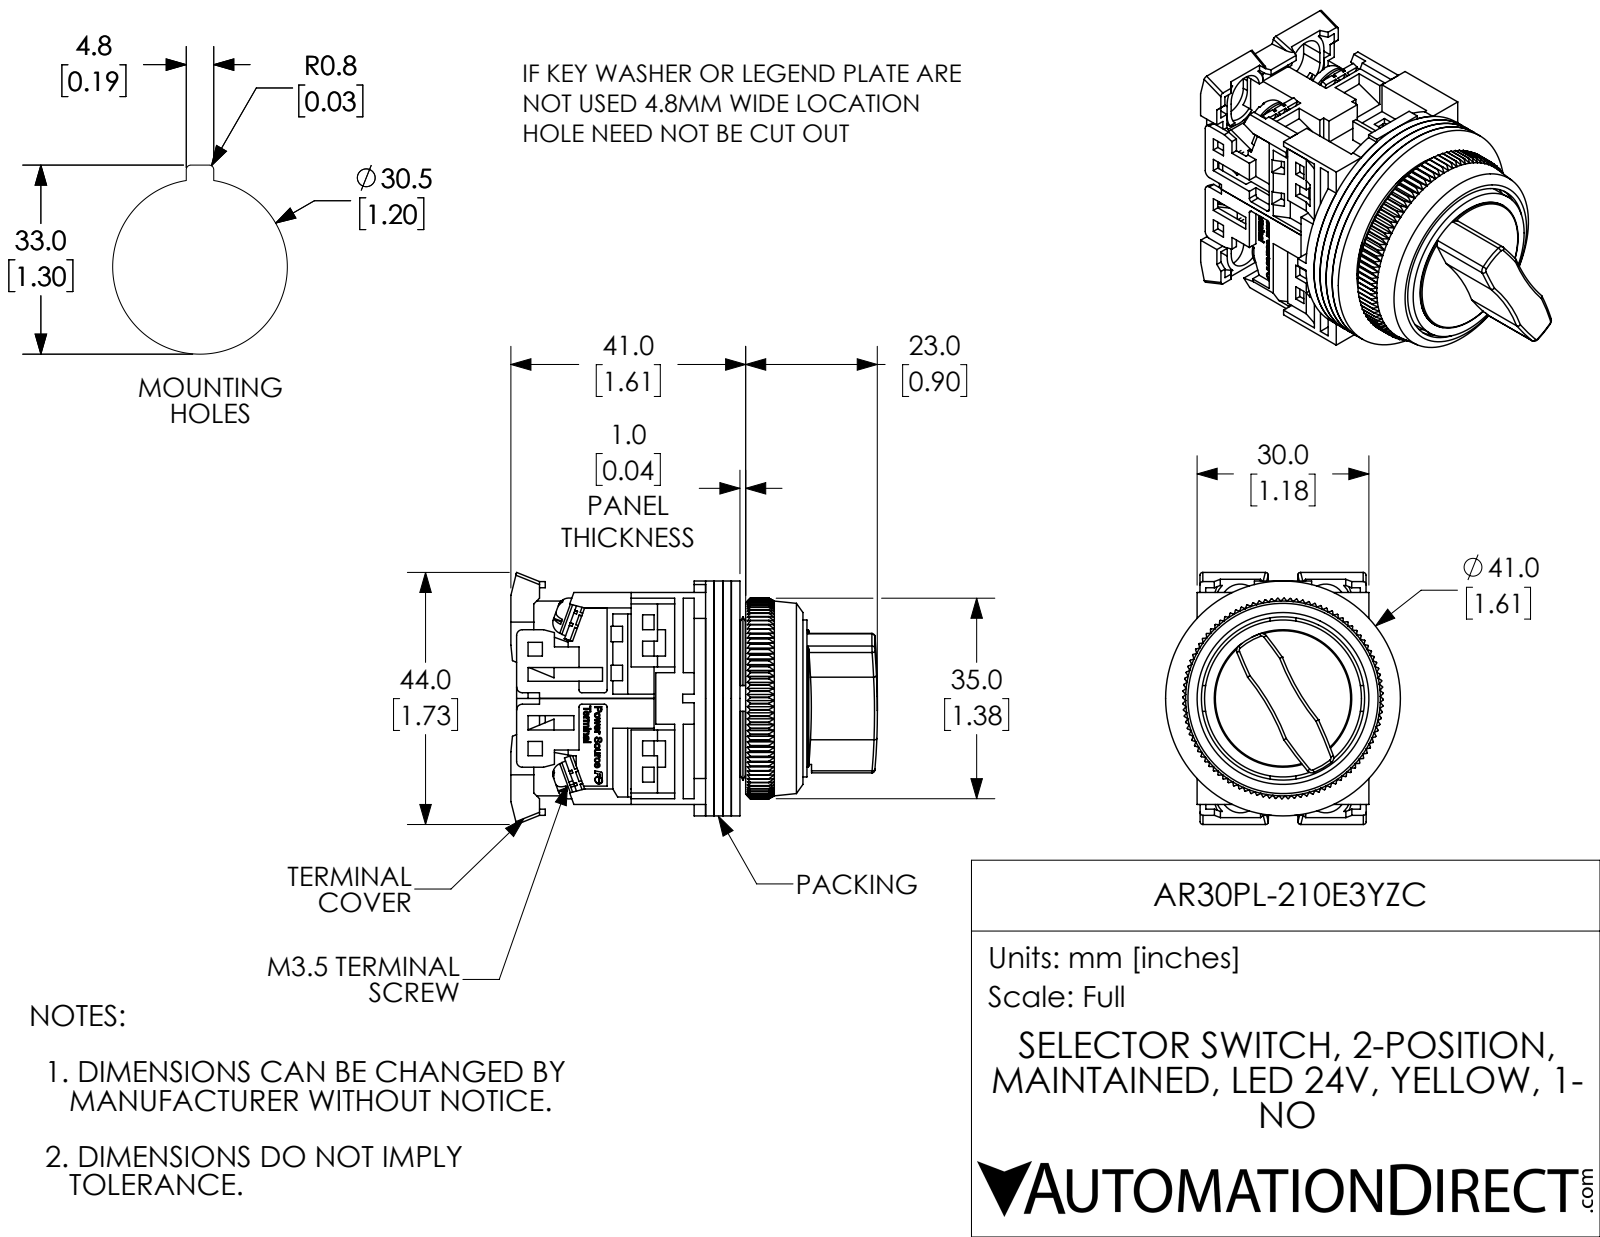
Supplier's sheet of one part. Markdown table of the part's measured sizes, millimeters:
| quantity | value |
| --- | --- |
| part name | AR30PL-210E3YZC |
| STEP written by | SolidWorks 2017 (AUTOMOTIVE_DESIGN) |
| units | millimeters |
| bodies | 25 solids, 2434 faces (1731 planar, 305 cylindrical, 398 other) |
| overall size | 64 × 44 × 41 |
| volume | 36 670 mm³ |
| surface area | 38 260 mm² |
| round holes (diameter × count) | 3.5 × 8, 3.6 × 4, 3 × 1, 12 × 1, 18 × 1, 19.5 × 1, 21 × 1, 28.5 × 1, 30 × 1, 31.8 × 1 |
| round bosses / shafts (diameter × count) | 6.6 × 4, 3.5 × 4, 1.6 × 2, 41 × 1, 29.2 × 1, 27.4 × 1, 24 × 1, 22.5 × 1 |
| partial cylindrical surfaces (radius × count) | 1.5 × 16, 0.5 × 12, 1 × 8, 3.5 × 4, 4.5 × 4, 3 × 2, 40 × 2, 75 × 2 |
| main face-to-face distances | 1.5, 3, 4.5, 1, 2, 36, 34.5, 20.6, 5, 0.5 |
| hole center spacings | 14.7, 15.5 |
